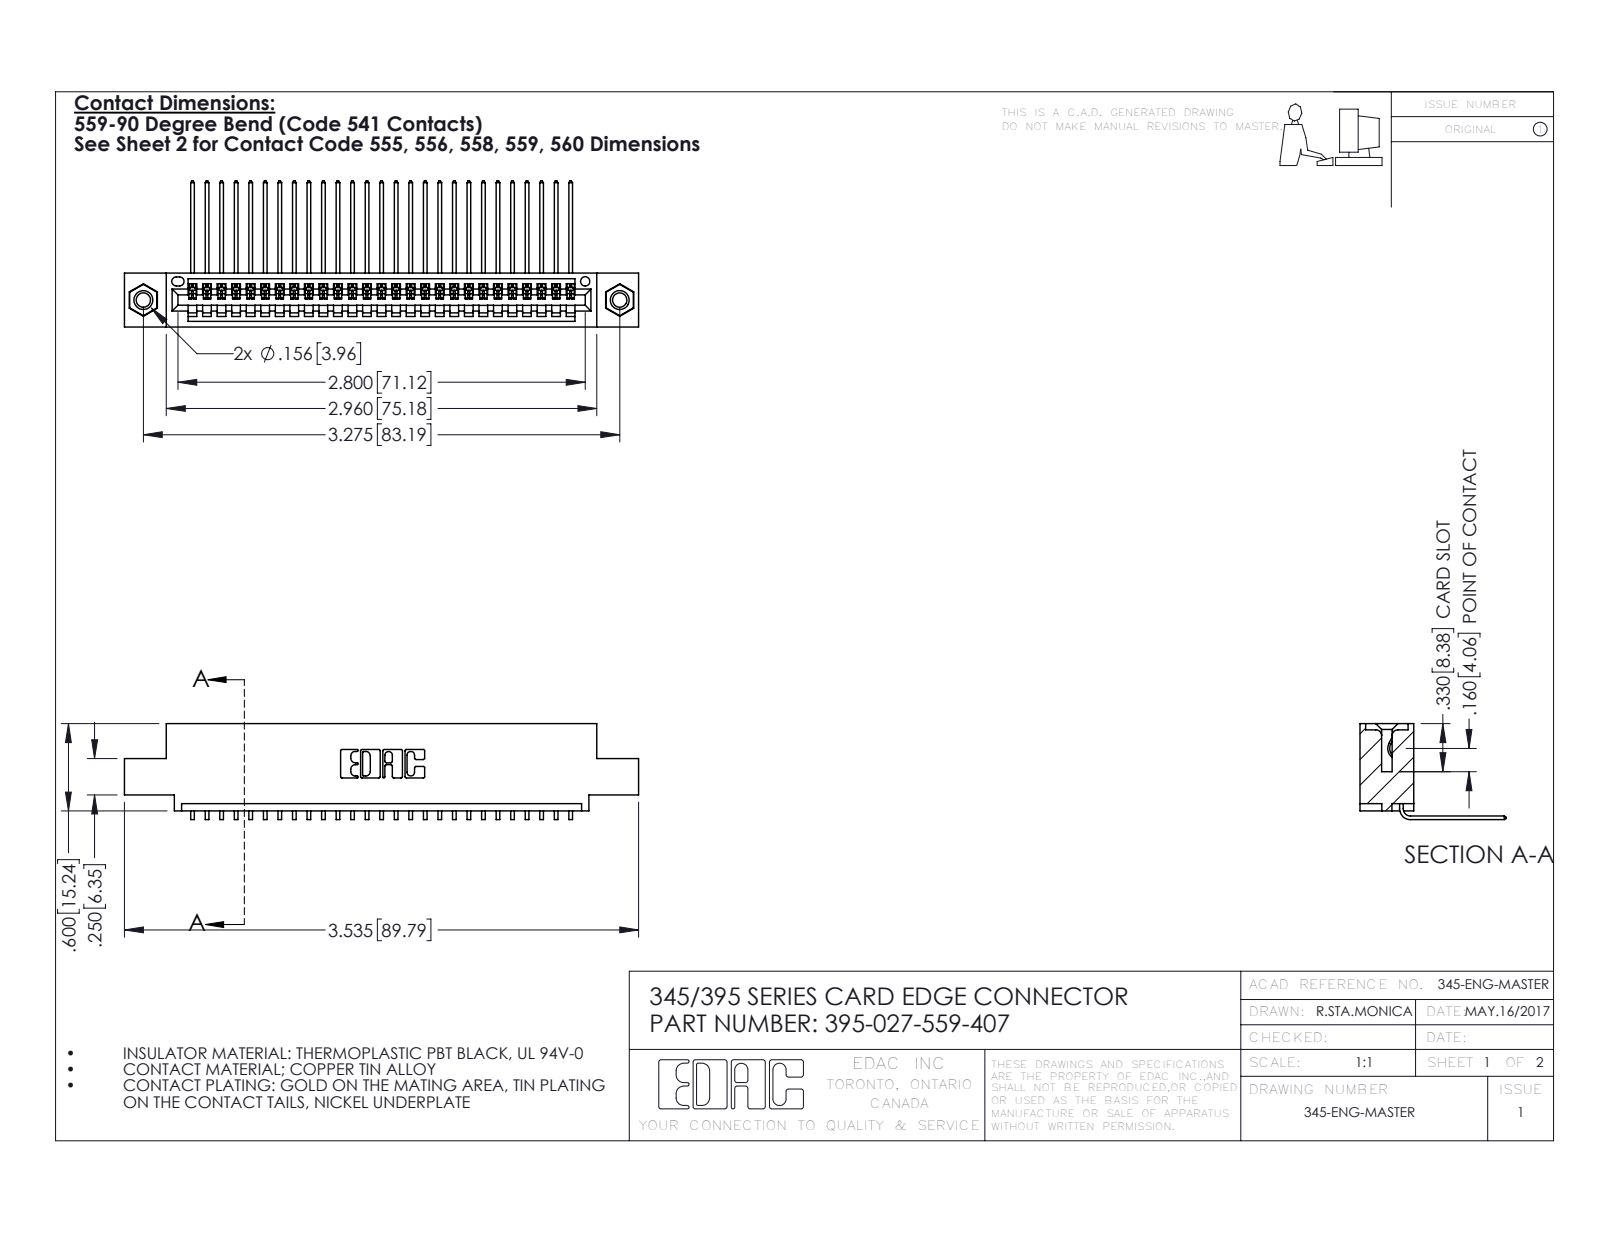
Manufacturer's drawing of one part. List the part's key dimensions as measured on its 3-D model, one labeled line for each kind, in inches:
Part name (STEP PRODUCT): 395-027-559-407; 345-250-001_345-250-005-103; 345-292-001_558 559 Tail - 1; 345 Part_0.110 Offset - 0.156 Dia-TI
STEP written by: SolidWorks 2016 (CONFIG_CONTROL_DESIGN)
Units: inches
Bodies: 30 solids, 1810 faces (1250 planar, 544 cylindrical, 16 other)
Overall size (bounding box): 3.535 × 1.005 × 0.659
Volume: 0.513 in³ · Surface area: 18 in²
Round holes (diameter × count): ⌀0.098 ×2, ⌀0.125 ×2, ⌀0.156 ×2, ⌀0.064 ×1
Round bosses / shafts (diameter × count): ⌀0.155 ×2
Partial cylindrical surfaces — rounded edges, fillets, slot ends (radius × count): R0.006 ×54, R0.01 ×22, R0.007 ×6, R0.031 ×6, R0.026 ×3, R0.031 ×2, R0.04 ×2, R0.014 ×1
Main face-to-face distances: 0.072, 0.298, 0.37, 0.2, 0.098, 0.272, 0.025, 0.225, 0.149, 0.072
Hole centre spacings: 0.27, 3.04, 3.275
